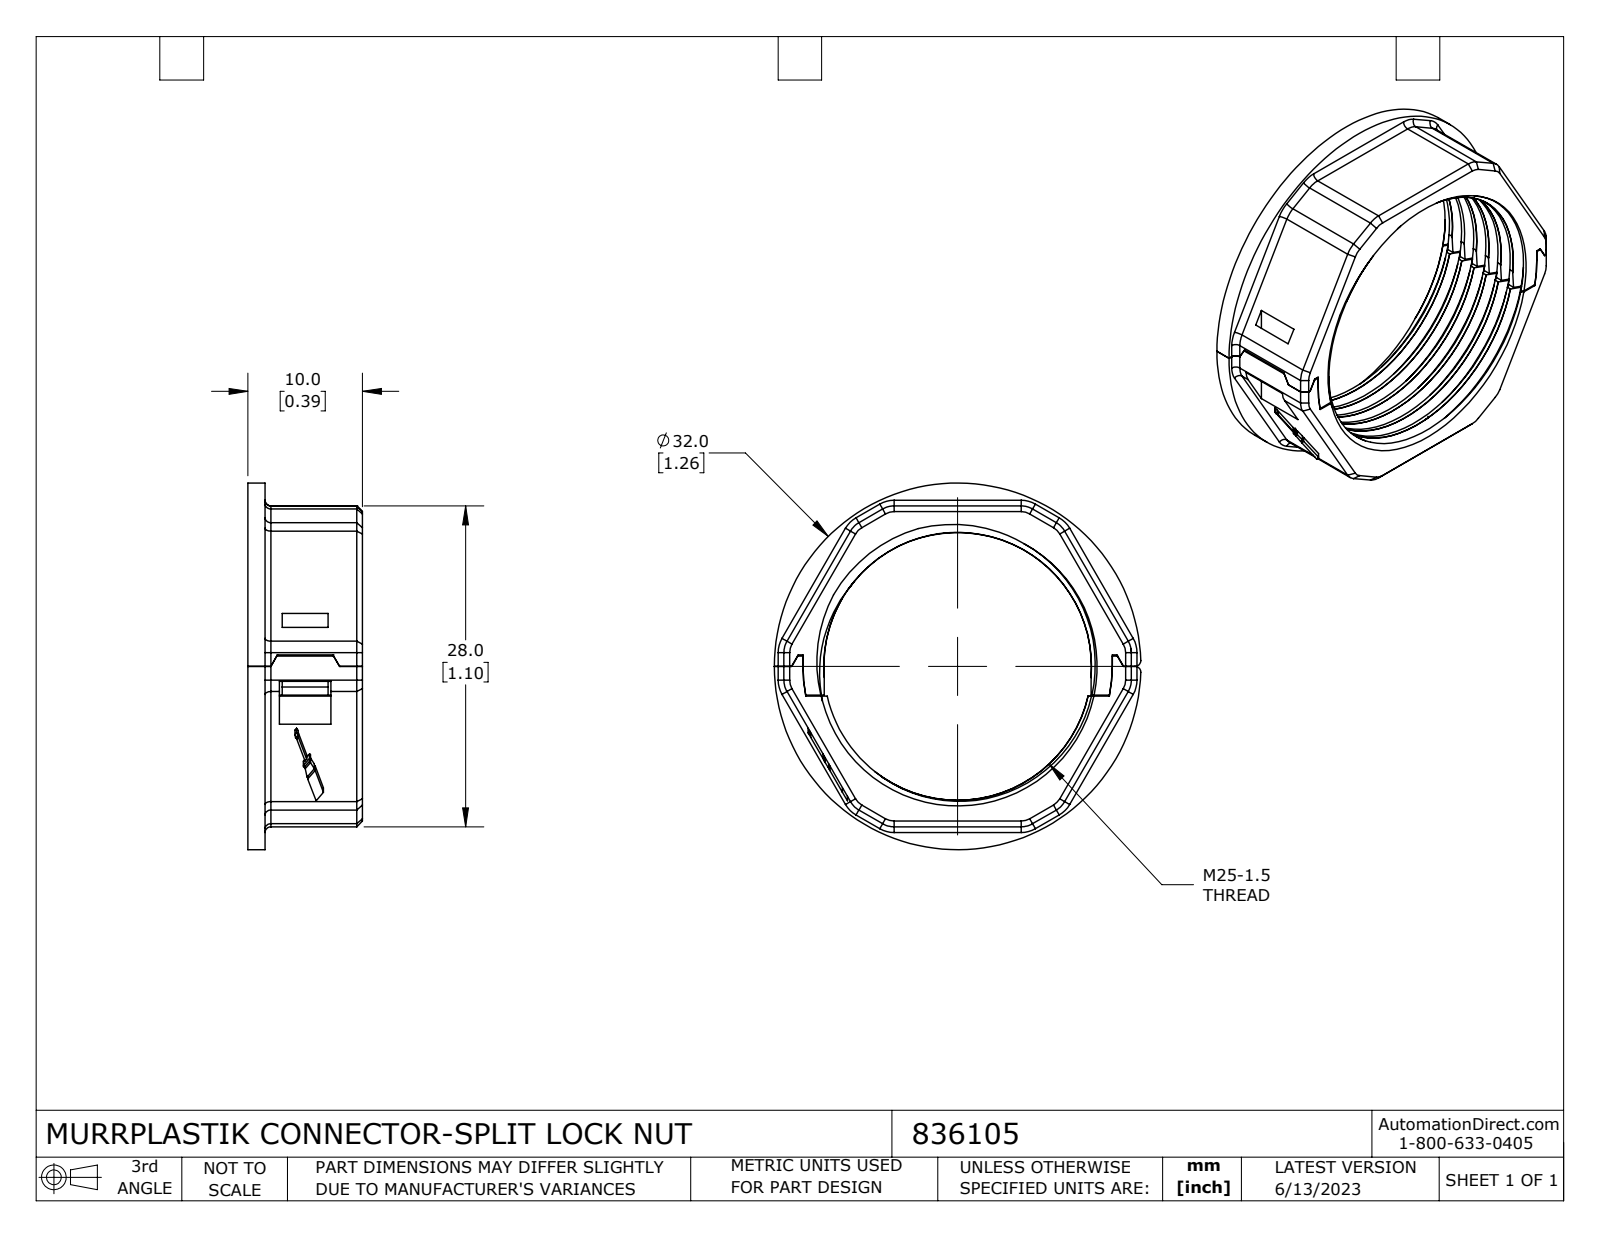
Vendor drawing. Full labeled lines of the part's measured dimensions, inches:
Part name (STEP PRODUCT): 836105
STEP written by: SolidWorks 2021 (CONFIG_CONTROL_DESIGN)
Units: inches
Bodies: 2 solids, 454 faces (225 planar, 85 cylindrical, 144 other)
Overall size (bounding box): 1.26 × 1.26 × 0.394
Volume: 0.137 in³ · Surface area: 4.867 in²
Round holes (diameter × count): ⌀0.236 ×1, ⌀0.92 ×1, ⌀0.984 ×1
Round bosses / shafts (diameter × count): ⌀1.26 ×1
Partial cylindrical surfaces — rounded edges, fillets, slot ends (radius × count): R0.02 ×14, R0.079 ×12, R0.531 ×1
Main face-to-face distances: 1.102, 0.394, 0.059, 0.335, 1.194, 1.063, 0.453, 0.591, 1.043, 0.066
